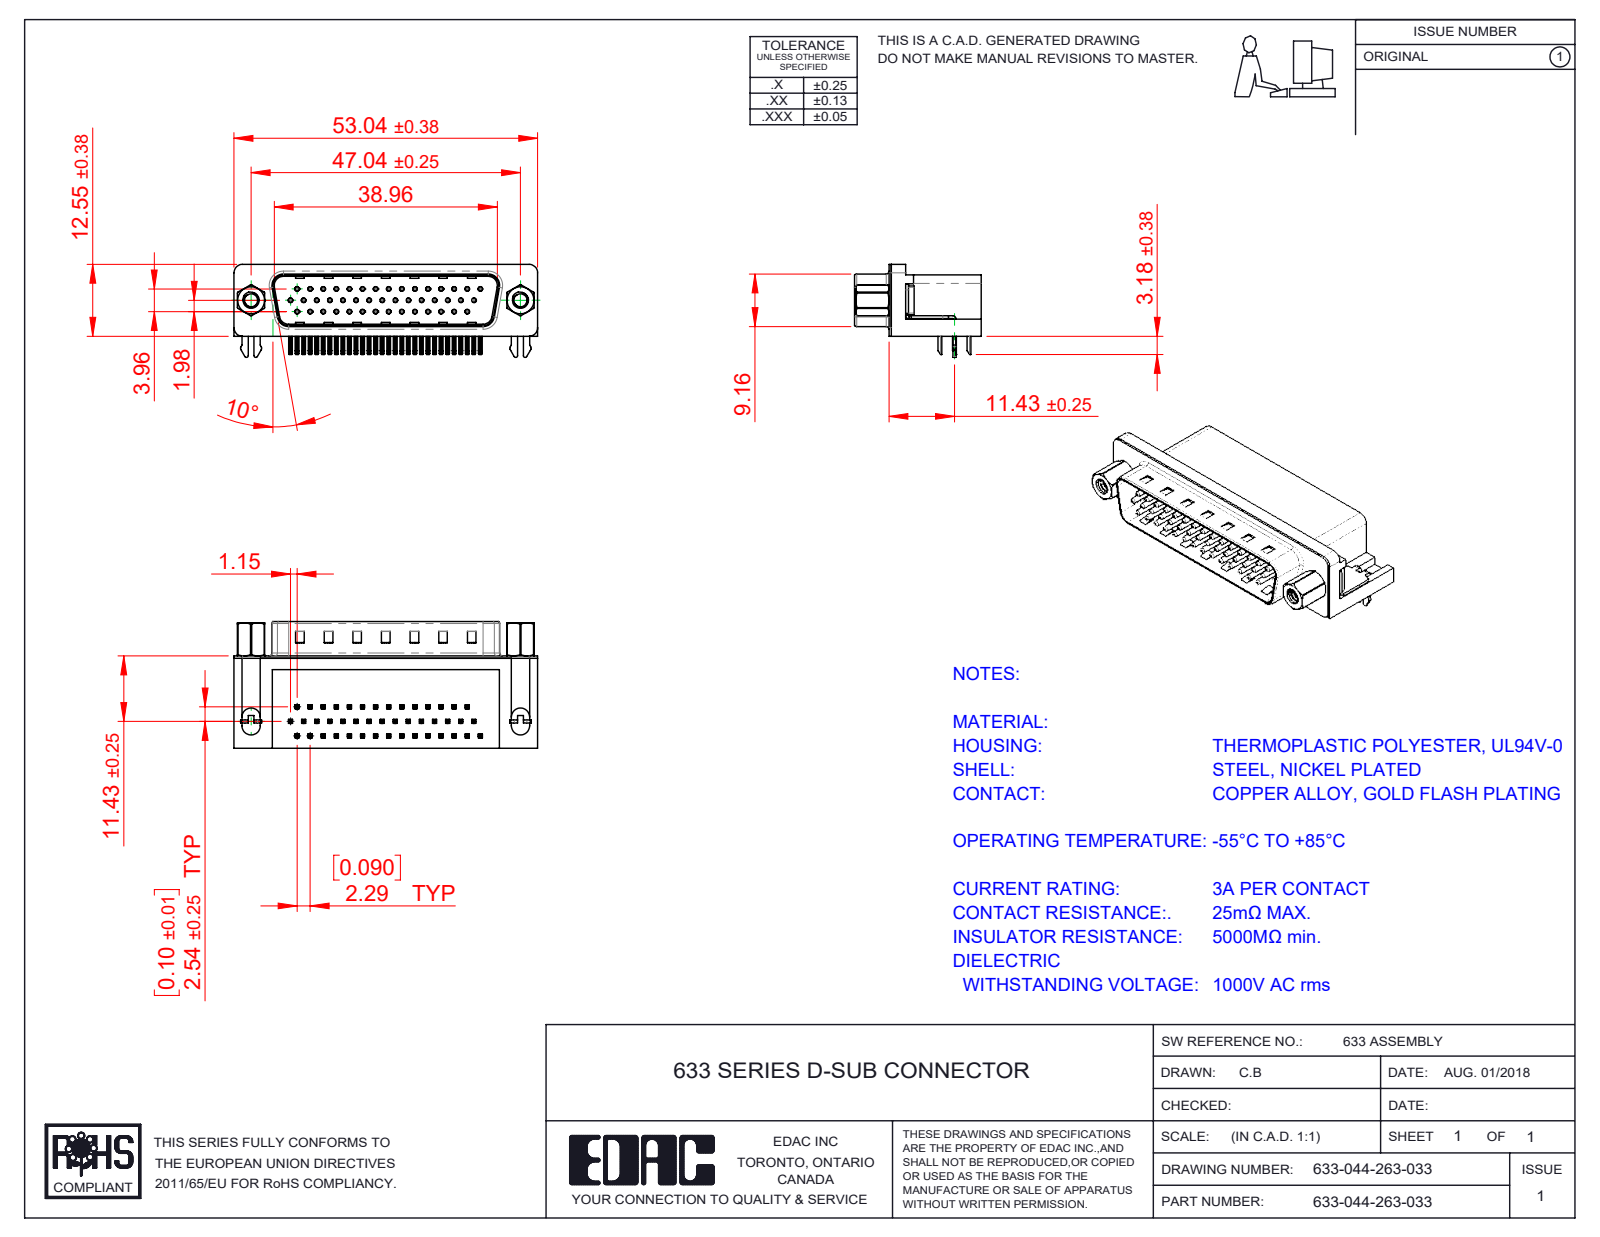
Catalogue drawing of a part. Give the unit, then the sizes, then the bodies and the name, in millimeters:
Units: millimetres
Overall size (bounding box): 53.04 × 22.1 × 16.25
Round holes (diameter × count): ⌀0.35 ×44, ⌀0.8 ×44, ⌀2.26 ×2, ⌀2.29 ×2, ⌀4 ×2, ⌀4.8 ×2, ⌀5 ×2
Round bosses / shafts (diameter × count): ⌀0.75 ×44, ⌀4.9 ×2, ⌀4.75 ×2, ⌀3.9 ×2, ⌀2.79 ×2
Partial cylindrical surfaces — rounded edges, fillets, slot ends (radius × count): R0.25 ×184, R0.12 ×88, R1 ×16, R0.5 ×14, R1.6 ×8, R1.5 ×7, R0.32 ×4, R0.9 ×4
Main face-to-face distances: 0.4, 10.35, 15.7, 8.76, 2.9, 2.5, 16.1, 2.1, 10.7, 2.54
Hole centre spacings: 2.29, 4.57, 4.58, 2.28, 6.87, 9.16, 11.45, 2.27
Volume: 8 316 mm³ · Surface area: 10 676 mm²
Bodies: 52 solids, 3850 faces (2371 planar, 1132 cylindrical, 347 other)
Part name (STEP PRODUCT): 633 Contact Bottom; 633 Shell_44 Contact; 633 Housing_44 Contact; 633-044-263-033 (+5 more)
STEP written by: SolidWorks 2016 (CONFIG_CONTROL_DESIGN)
